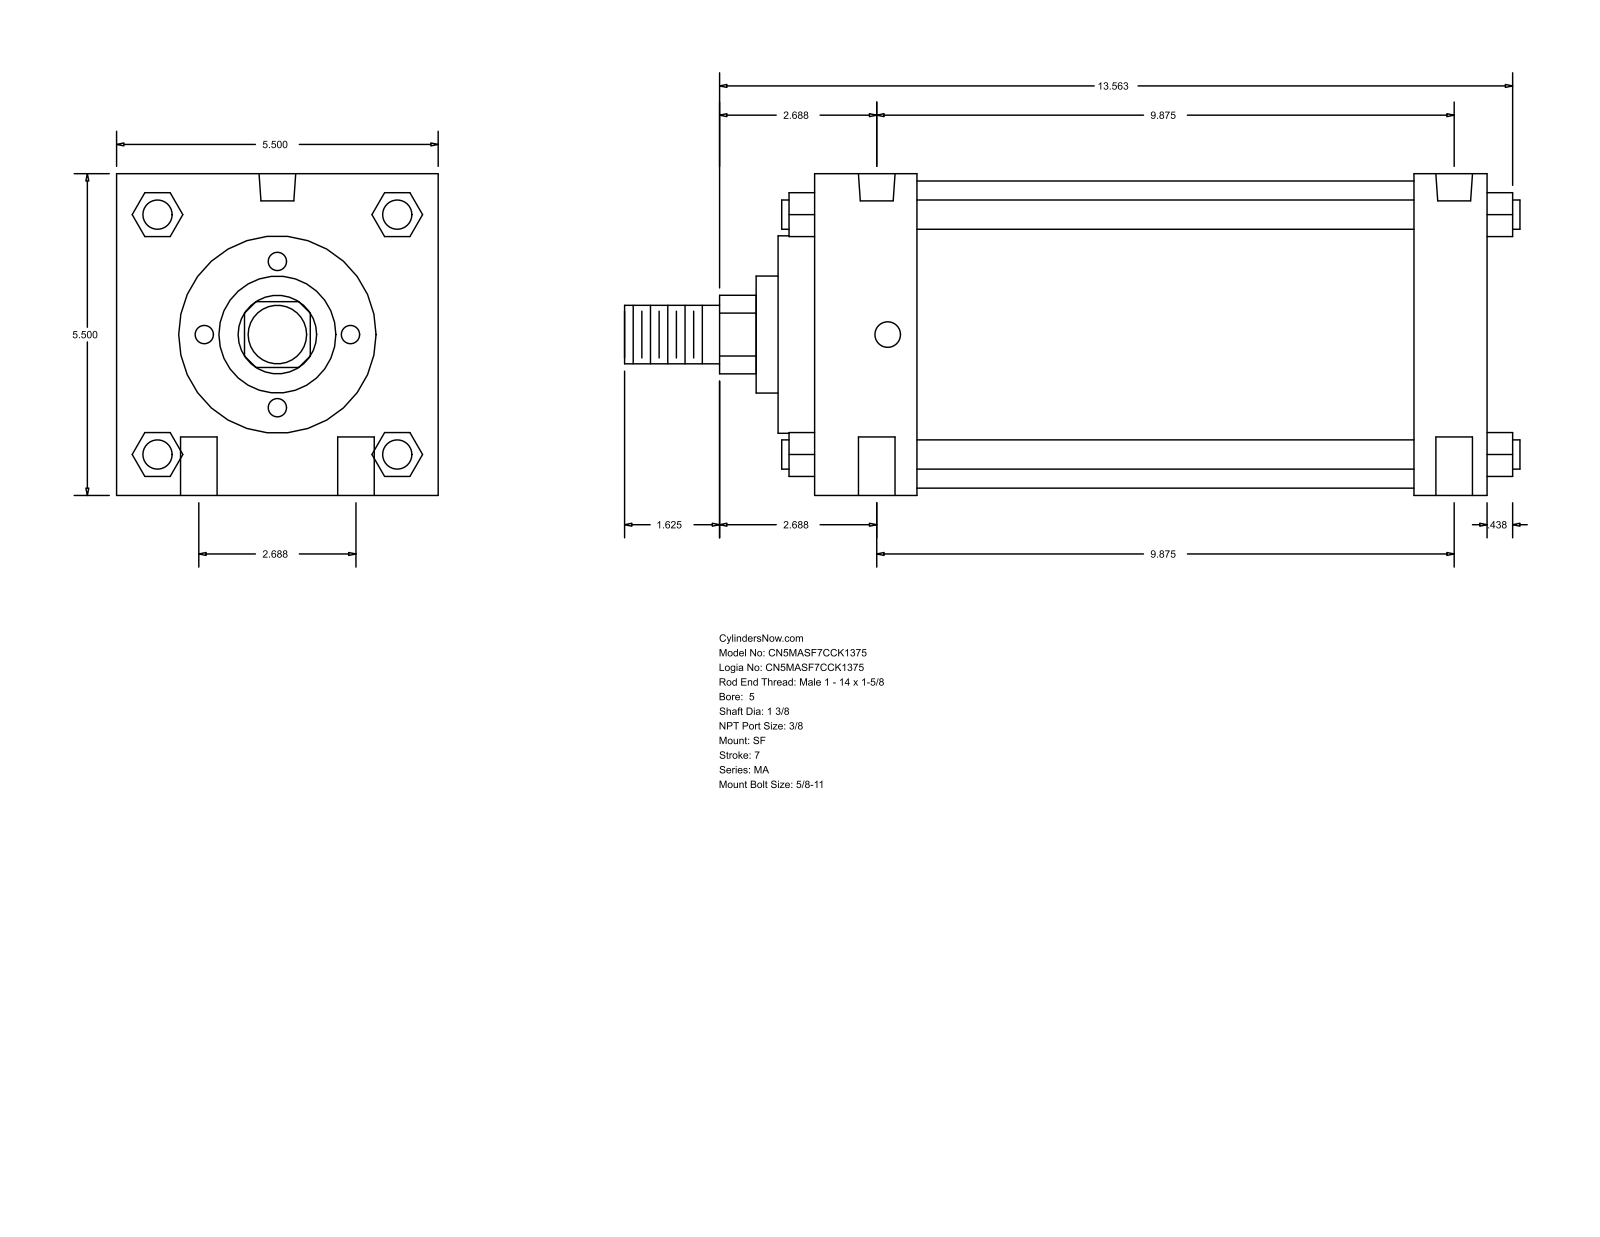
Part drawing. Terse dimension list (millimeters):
name: MA_SF__0500_1.375
written by: GSSL Pune (CONFIG_CONTROL_DESIGN)
unit: mm
bodies: 0 solids, 126 faces (95 planar, 31 cylindrical, 0 other)
size: 388.94 × 139.7 × 139.7
holes: 4× ⌀15.88, 2× ⌀11.11, 2× ⌀15.93
bosses: 4× ⌀12.7, 1× ⌀133.35, 1× ⌀85.72, 1× ⌀50.8, 1× ⌀34.92, 1× ⌀25.4
rounds: 1× R17.06
face distances: 139.7, 292.11, 44.45, 260.35, 215.9, 247.66, 31.76, 15.87, 60.32, 276.22
hole spacings: 34.13, 253.14, 250.83, 68.26, 259.95, 241.29
